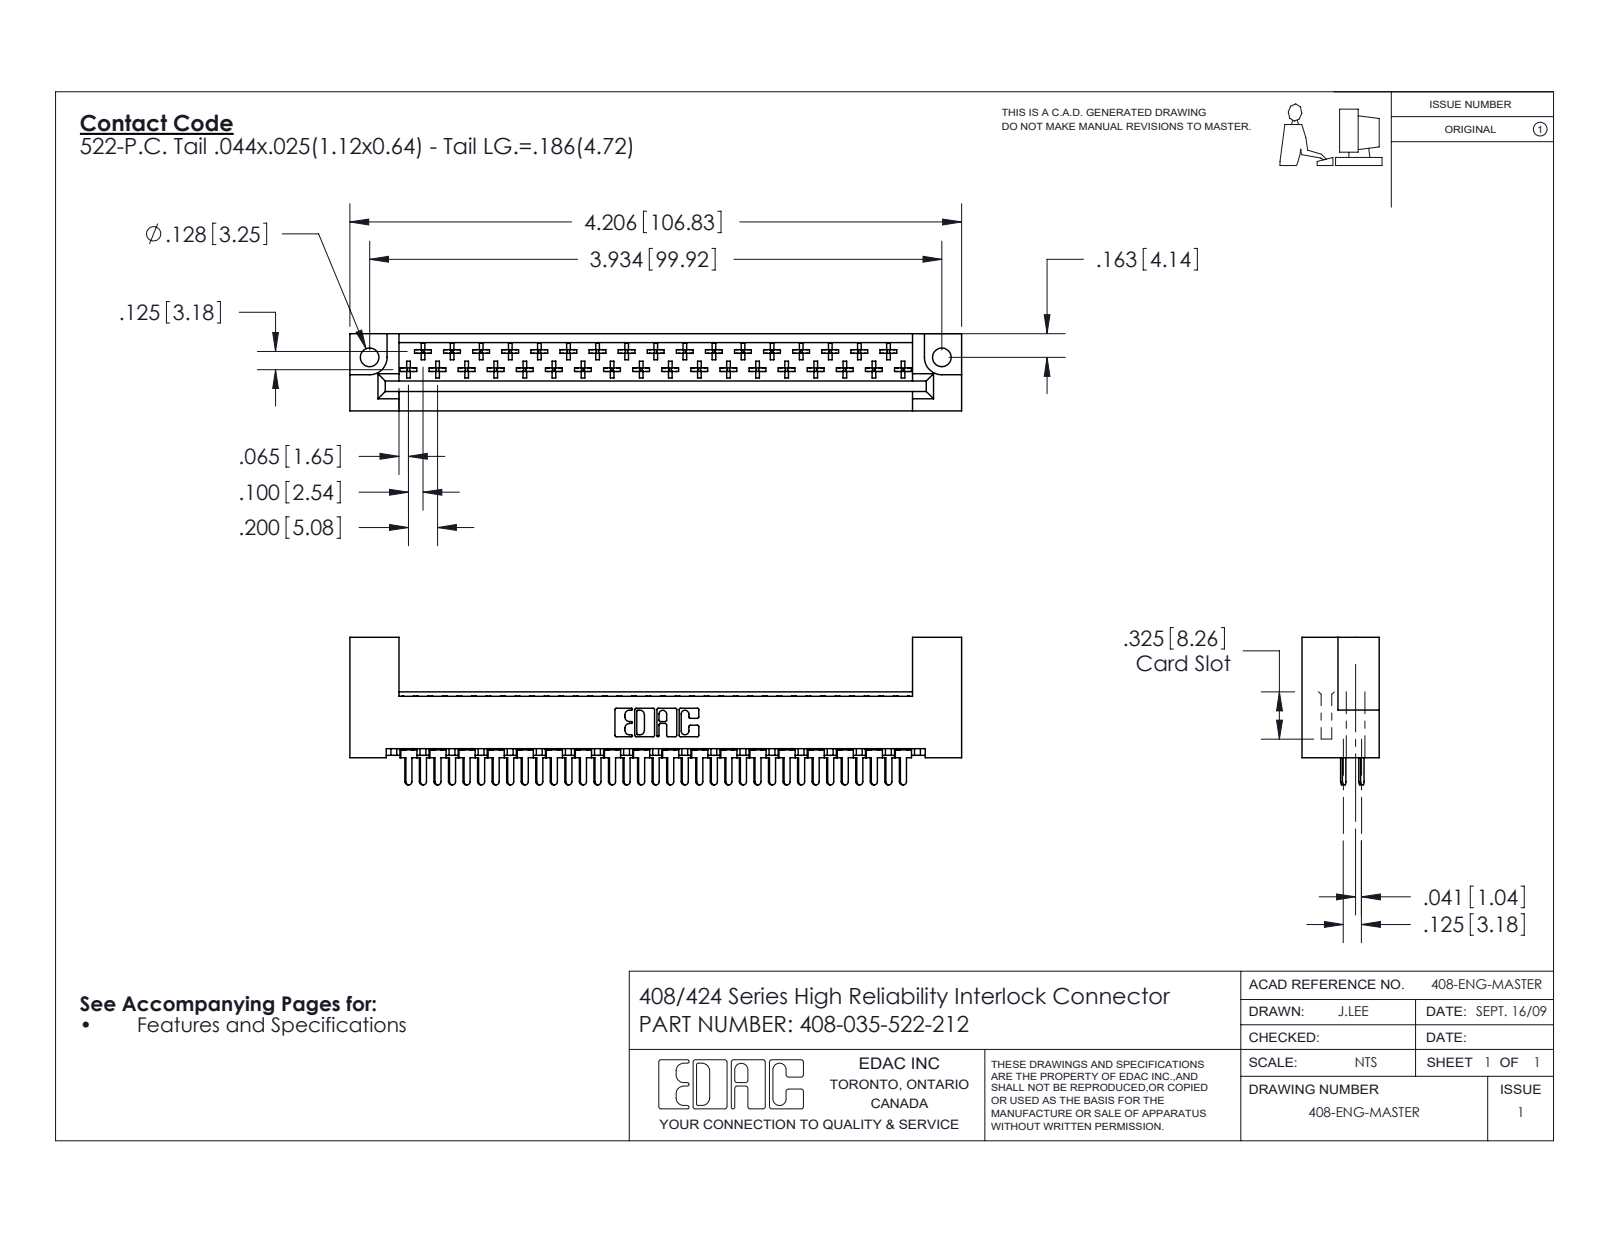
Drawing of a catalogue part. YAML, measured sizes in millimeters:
part_name: "408 Part_035 - 2; 408-290-001_408-290-122; 408-035-522-212"
step_written_by: "SolidWorks 2016 (CONFIG_CONTROL_DESIGN)"
units: millimeters
bodies: {solids: 36, faces: 2064, planar: 1559, cylindrical: 365, other: 140}
overall_size: [106.8, 25.8, 13.5]
volume: 13400
surface_area: 15500
round_holes:
  - {diameter: 3.3, count: 2}
partial_cylinders:
  - {radius: 0.3, count: 210}
  - {radius: 0.5, count: 37}
  - {radius: 0.6, count: 35}
  - {radius: 0.3, count: 22}
  - {radius: 0.2, count: 6}
  - {radius: 0.8, count: 6}
  - {radius: 0.7, count: 3}
  - {radius: 3, count: 2}
face_to_face_distances: [13.5, 3.2, 2.5, 0.6, 0.6, 9.2, 6, 6.6, 10.1, 5.5]
hole_center_spacings: [99.9]
